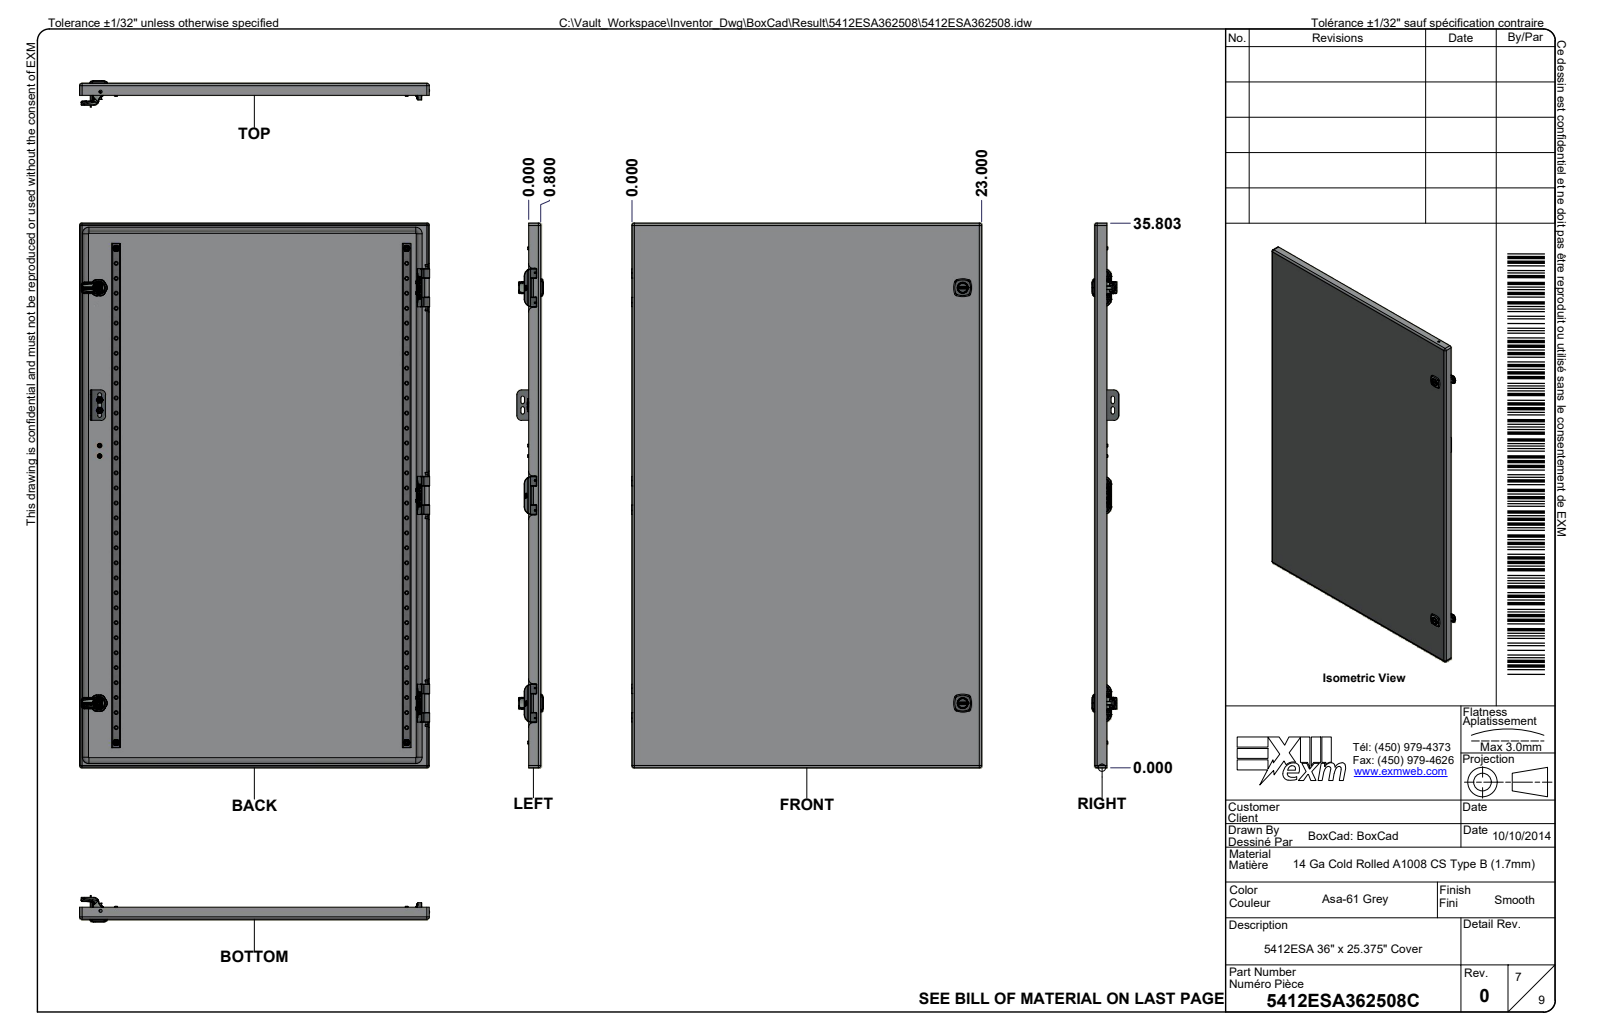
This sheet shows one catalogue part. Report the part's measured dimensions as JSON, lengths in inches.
{"part_name": "5412ESA362508; 5412ESA362508B; 5412ESA362508B-P; STK-Q-16005 (+8 more)", "step_written_by": "Autodesk Inventor 2024 (AUTOMOTIVE_DESIGN)", "units": "inches", "bodies": {"solids": 86, "faces": 14449, "planar": 4039, "cylindrical": 3739, "other": 6671}, "overall_size": [36, 25.378, 9.295], "volume_in3": 277.7, "surface_area_in2": 8215, "round_holes": [[0.165, 64], [0.03, 15], [0.043, 12], [0.315, 12], [0.201, 11], [0.178, 6], [0.197, 6], [0.268, 6], [0.27, 6], [0.29, 6], [0.311, 6], [0.39, 4]], "round_bosses_or_shafts": [[0.237, 64], [0.03, 15], [0.232, 14], [0.039, 12], [0.177, 8], [0.717, 6], [0.374, 6], [0.311, 6]], "partial_cylinders_radius": [[0.02, 315], [0.01, 169], [0.039, 143], [0.008, 124], [0.012, 50], [0.016, 44], [0.031, 32], [0.004, 26]], "face_to_face_distances": [0.053, 0.068, 9.052, 8.998, 9.12, 9.067, 0.927, 0.874, 8.124, 8.193], "hole_center_spacings": [13.652, 1.969, 27.303, 0.35, 0.735, 1.052, 1.385, 0.984]}
